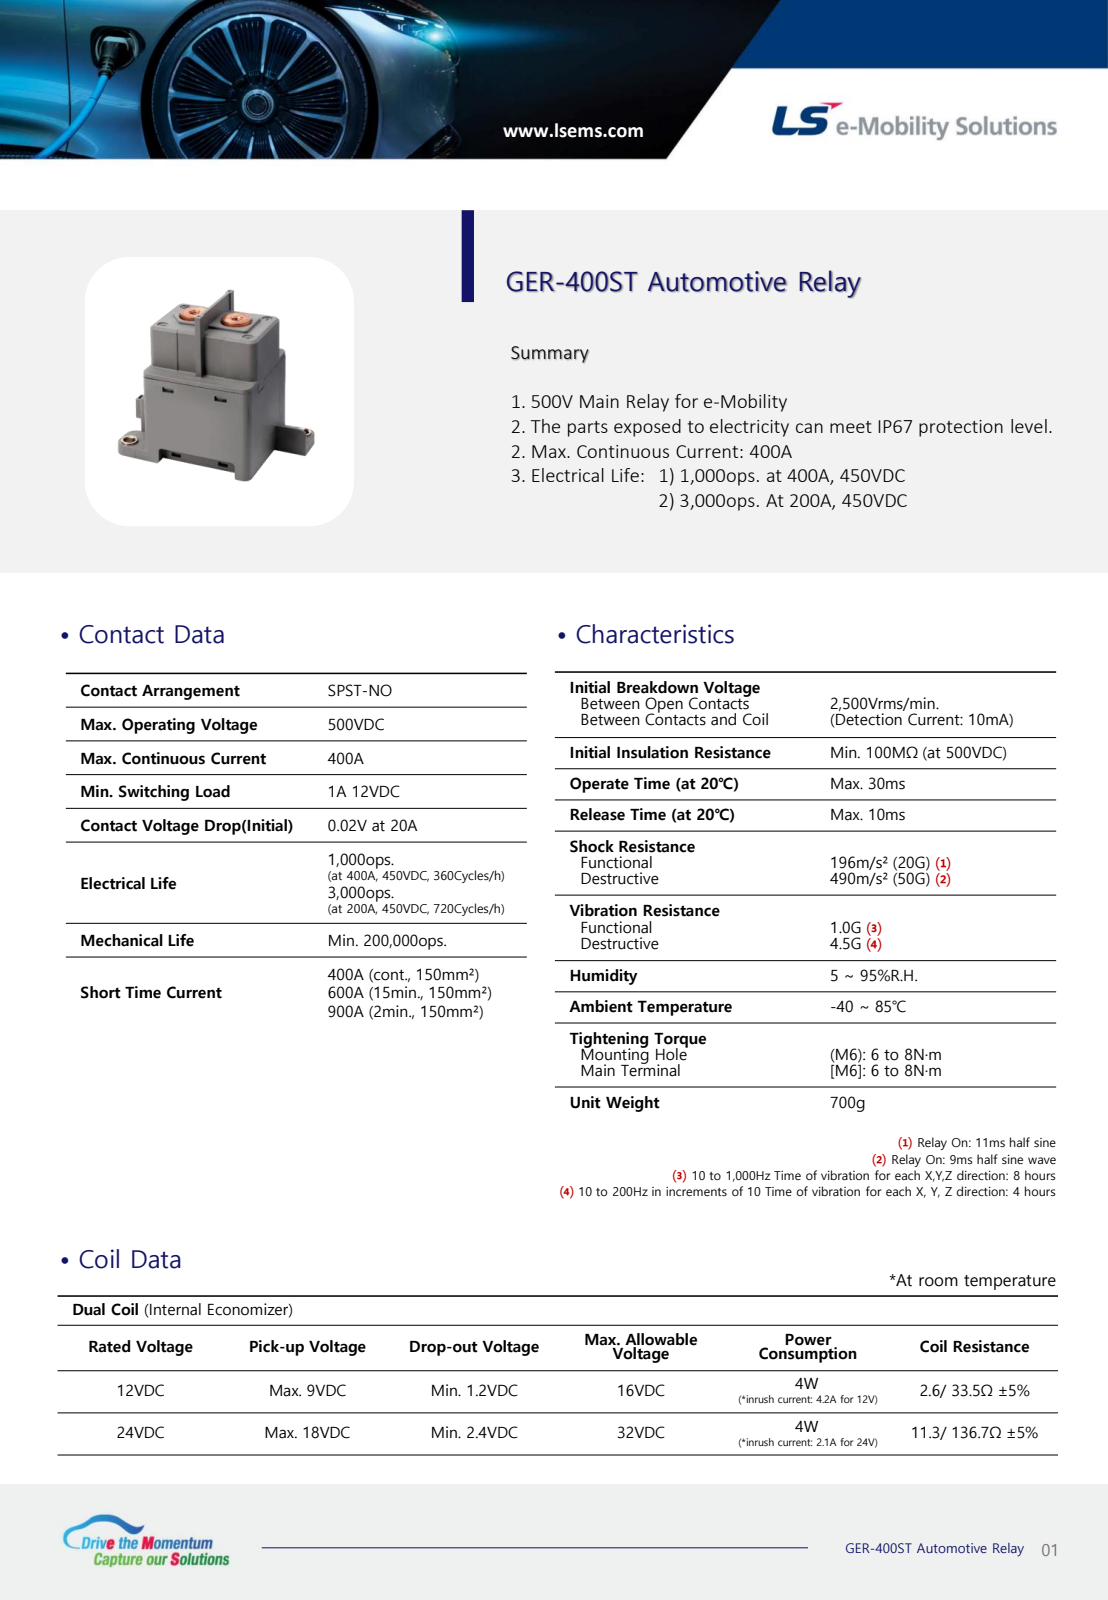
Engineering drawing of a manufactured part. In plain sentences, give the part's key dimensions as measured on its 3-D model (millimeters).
The part is named "72316605002_72316605004_72316605003_72316605005_AllCATPart". Its 3-D file was written by "CATIA V5 STEP AP214 (AUTOMOTIVE_DESIGN)". It is 9 solids with 1982 faces: 869 planar, 654 cylindrical and 459 other. Overall it measures 100 by 91 by 58.2 millimeters. Its volume is 67 138 cubic millimeters and its surface area 73 868 square millimeters. Round holes: 6 of diameter 6, 2 of diameter 0.8, 2 of diameter 1, 2 of diameter 1.5, 2 of diameter 1.8, 2 of diameter 6.2, 2 of diameter 6.5, 2 of diameter 9, 2 of diameter 13.8, 2 of diameter 16.5, 2 of diameter 23. Round bosses or shafts: 2 of diameter 16, 2 of diameter 10, 2 of diameter 9.4, 2 of diameter 8.4. Partial cylindrical surfaces (rounded edges, fillets, slot ends): 238 of radius 0.5, 47 of radius 0.3, 31 of radius 1, 24 of radius 0.2, 16 of radius 2, 10 of radius 4, 8 of radius 2.2, 3 of radius 6.5. The main face-to-face distances are 1.8, 61.2, 56.2, 9.2, 6.3, 54.9, 63, 58, 59.4, 47. The hole center spacings are 18.77, 24.01, 25.83, 40.03, 42.61, 20.36, 28, 38.3.
